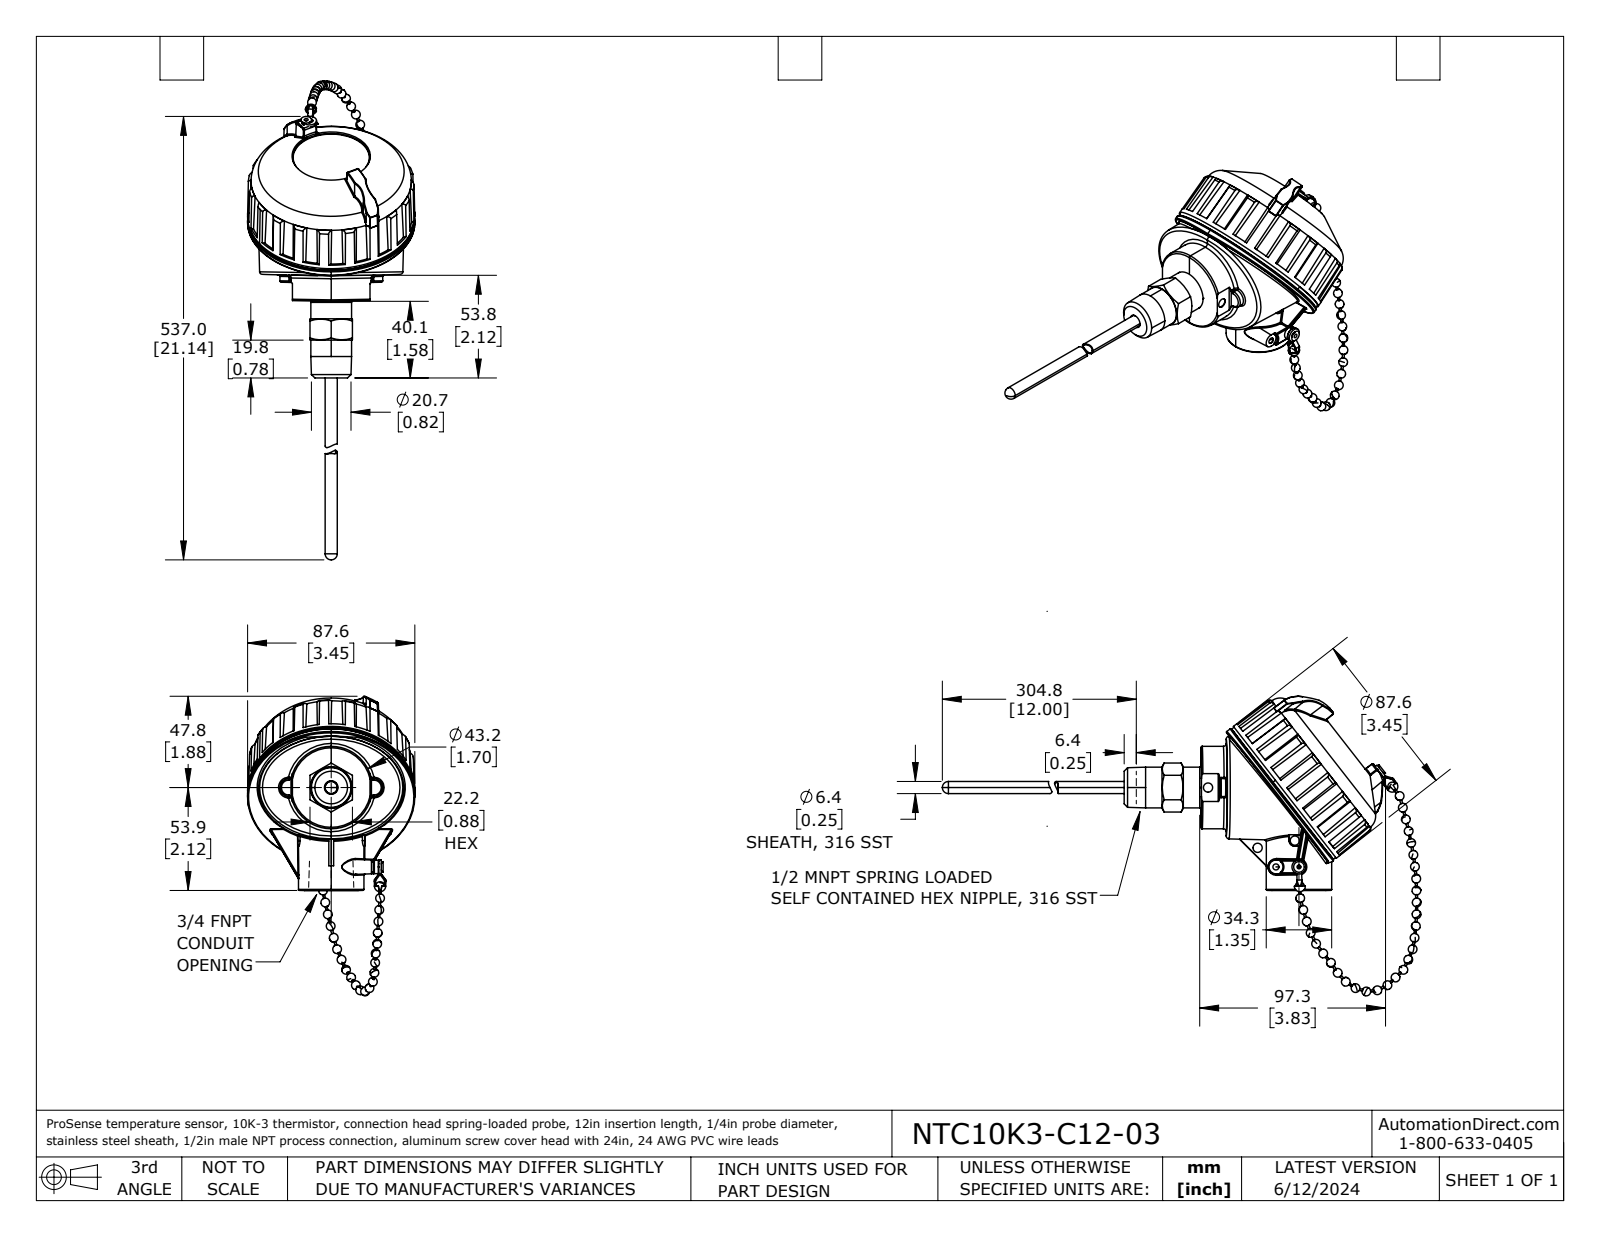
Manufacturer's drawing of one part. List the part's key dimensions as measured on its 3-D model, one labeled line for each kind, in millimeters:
Part name (STEP PRODUCT): NTC10K3-C12-03
STEP written by: SolidWorks 2021 (AUTOMOTIVE_DESIGN)
Units: millimetres
Bodies: 10 solids, 991 faces (234 planar, 195 cylindrical, 562 other)
Overall size (bounding box): 453.9 × 156.9 × 87.6
Volume: 154 900 mm³ · Surface area: 85 610 mm²
Round holes (diameter × count): ⌀4.8 ×3, ⌀2 ×2, ⌀3.7 ×2, ⌀3.2 ×1, ⌀4.2 ×1, ⌀5.3 ×1, ⌀6.6 ×1, ⌀11.1 ×1, ⌀11.8 ×1, ⌀22.6 ×1, ⌀76.3 ×1, ⌀76.9 ×1
Round bosses / shafts (diameter × count): ⌀1 ×31, ⌀7.4 ×2, ⌀3.1 ×2, ⌀87.6 ×1, ⌀86.5 ×1, ⌀79.3 ×1, ⌀76 ×1, ⌀43.2 ×1
Partial cylindrical surfaces — rounded edges, fillets, slot ends (radius × count): R0.5 ×21, R0.8 ×11, R0.4 ×6, R1.5 ×5, R1.6 ×2, R4.7 ×2, R3.7 ×1
Main face-to-face distances: 36.1, 37.7, 1.6, 3.6, 39.6, 41.2, 13.3, 13.3, 14.9, 27.6
Hole centre spacings: 25, 1.8, 12.1, 13.9, 13.9, 17, 19.9, 23.9
